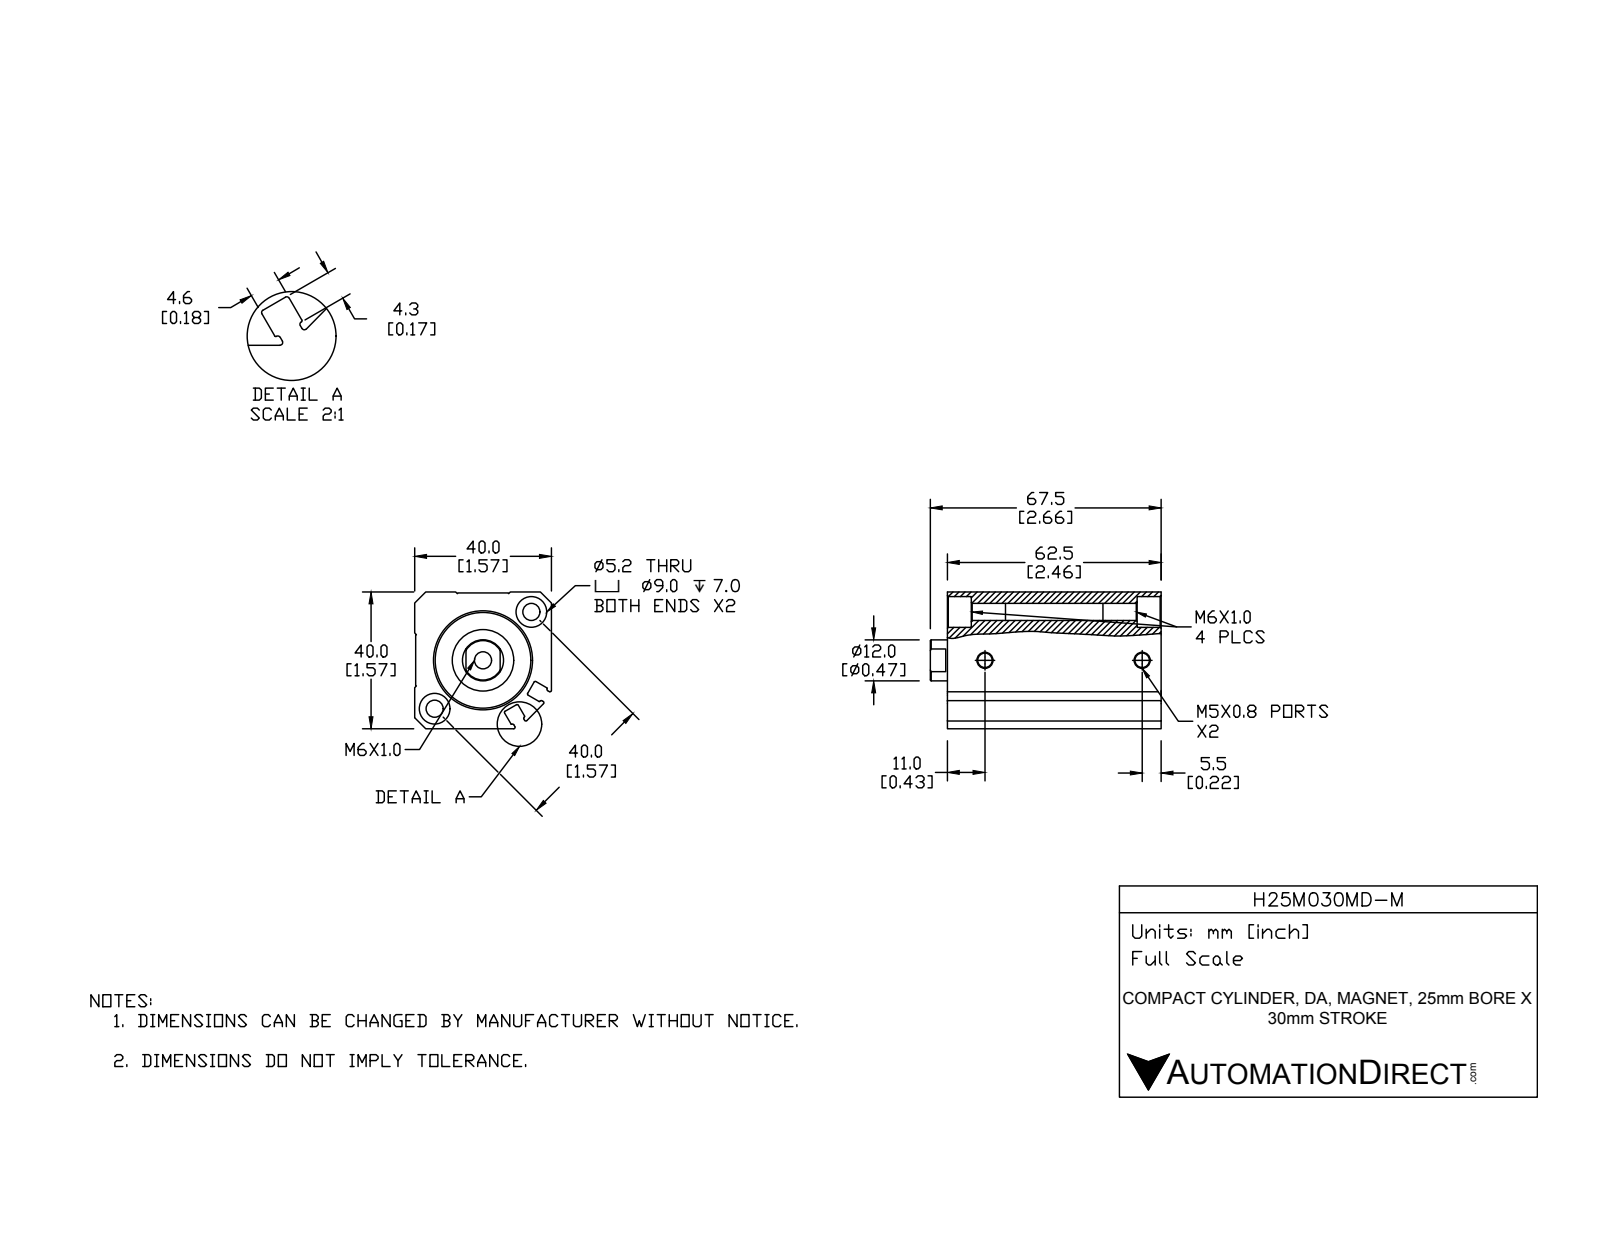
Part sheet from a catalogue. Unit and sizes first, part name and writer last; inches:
Units: inches
Overall size (bounding box): 2.657 × 1.575 × 1.575
Round holes (diameter × count): ⌀0.197 ×3, ⌀0.165 ×2, ⌀0.354 ×2, ⌀0.472 ×1, ⌀0.63 ×1, ⌀0.984 ×1, ⌀1.102 ×1
Round bosses / shafts (diameter × count): ⌀0.709 ×1, ⌀0.551 ×1
Partial cylindrical surfaces — rounded edges, fillets, slot ends (radius × count): R0.016 ×12, R0.008 ×4
Main face-to-face distances: 1.575, 1.563, 0.157, 2.461, 2.303, 0.055, 0.102, 2.406, 0.181, 2.028
Hole centre spacings: 0.787, 1.574, 1.811
Volume: 4.588 in³ · Surface area: 40.07 in²
Bodies: 2 solids, 141 faces (53 planar, 55 cylindrical, 33 other)
Part name (STEP PRODUCT): H25M030MD-M; H25M030MD-M-PISTON; H25M030MD-M-BODY
STEP written by: SolidWorks 2015 (CONFIG_CONTROL_DESIGN)
